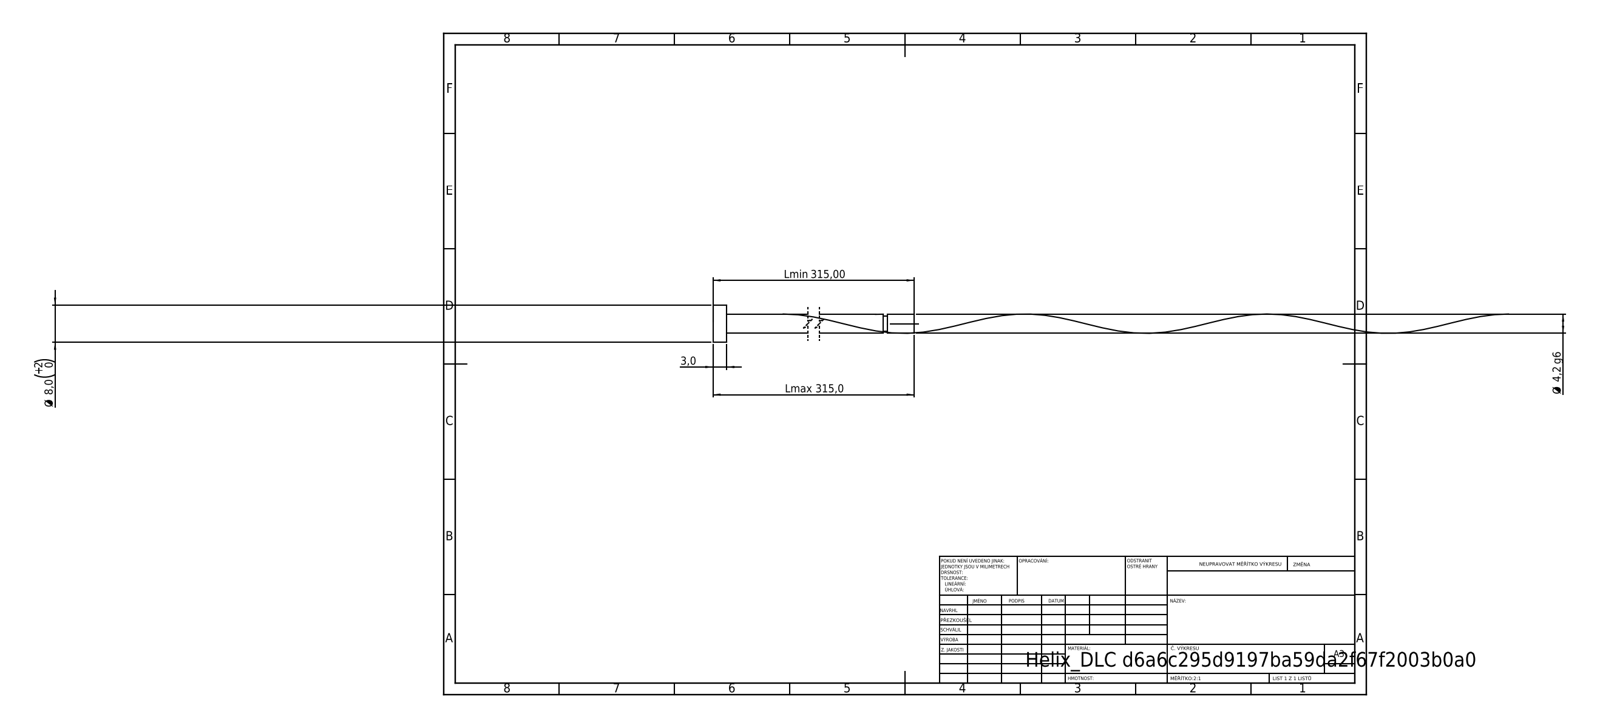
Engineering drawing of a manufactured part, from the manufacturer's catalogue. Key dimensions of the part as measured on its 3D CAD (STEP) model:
STEP written by: SolidWorks 2019 (CONFIG_CONTROL_DESIGN)
Units: millimetres
Bodies: 1 solid, 16 faces (6 planar, 9 cylindrical, 1 other)
Overall size (bounding box): 315 × 8 × 8
Volume: 5 397 mm³ · Surface area: 5 751 mm²
Round bosses / shafts (diameter × count): ⌀8 ×1, ⌀4.2 ×1, ⌀3.36 ×1
Main face-to-face distances: 3, 315, 312, 309.13, 306.13, 5.87, 308.29, 305.29, 0.84, 6.71
